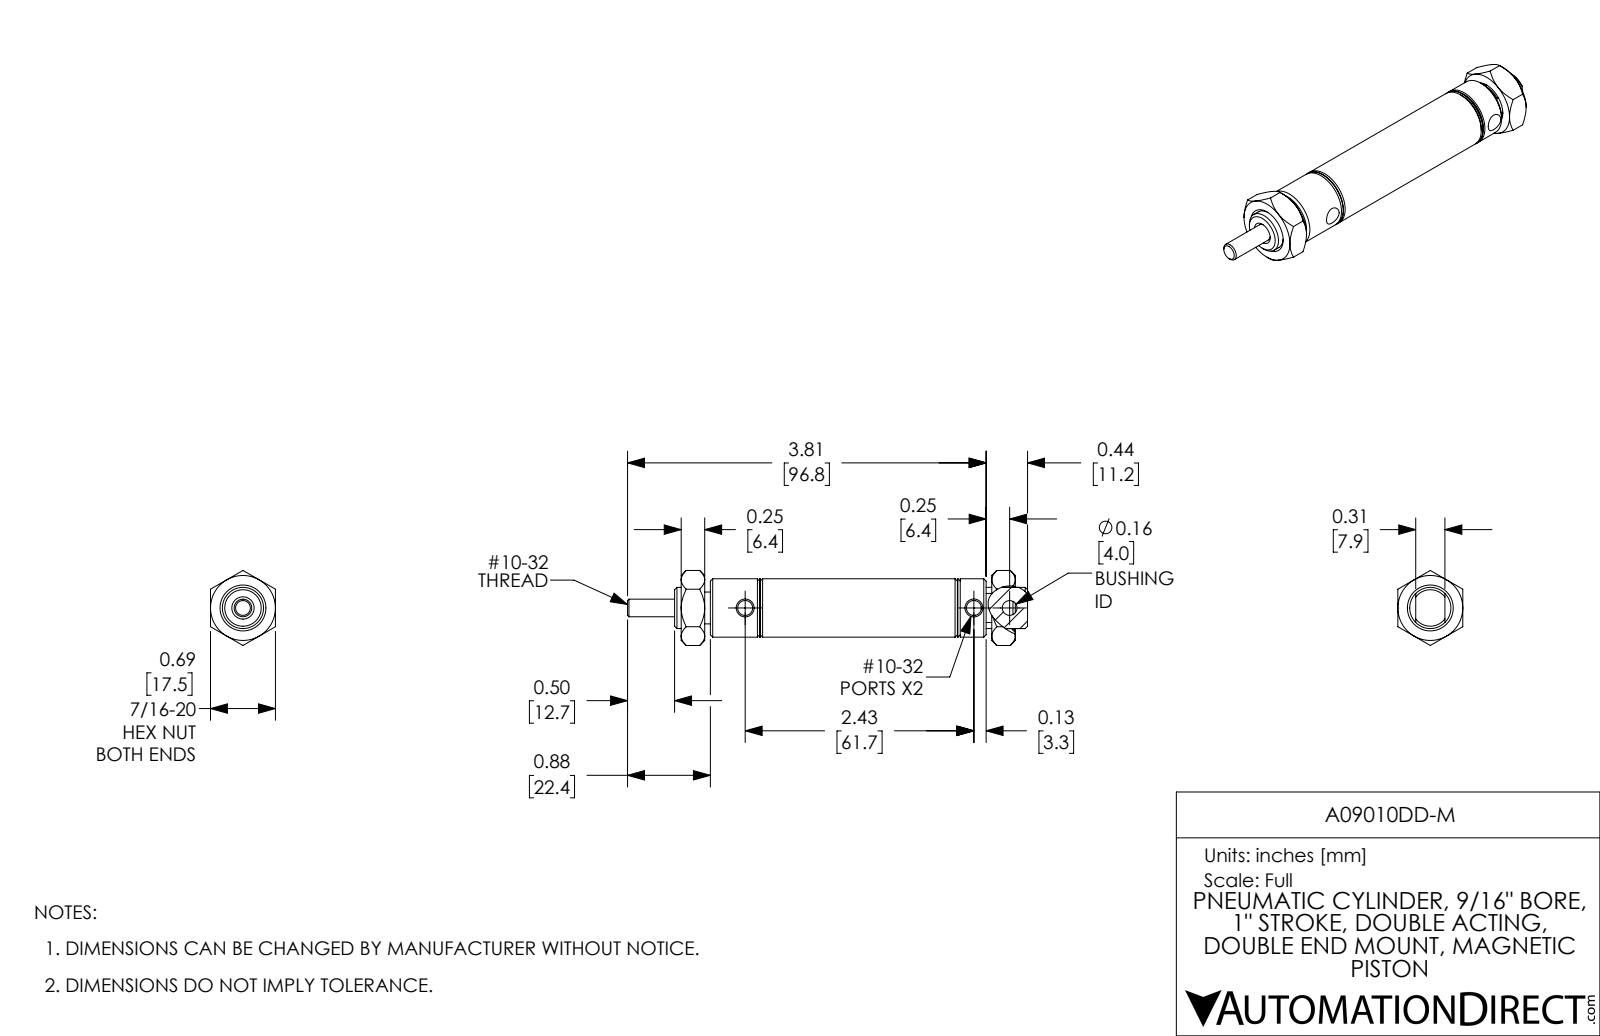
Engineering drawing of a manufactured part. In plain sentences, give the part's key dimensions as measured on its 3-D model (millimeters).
The part is named "A09010DD-M; A09010DD-M_Mounting Nut_D-154; A09010DD-M-Rod; A09010DD-M-MainBody". Its 3-D file was written by "SolidWorks 2017 (AUTOMOTIVE_DESIGN)". It is 4 solids with 151 faces: 36 planar, 46 cylindrical and 69 other. Overall it measures 108 by 20.2 by 17.5 millimeters. Its volume is 14 400 cubic millimeters and its surface area 11 380 square millimeters. Round holes: 2 of diameter 4, 2 of diameter 4.8, 1 of diameter 4, 1 of diameter 4, 1 of diameter 4.7, 1 of diameter 14.3. Round bosses or shafts: 1 of diameter 15.7, 1 of diameter 11.1, 1 of diameter 8.6. The main face-to-face distances are 17.5, 12.7, 6.4, 83.8, 18.2, 56.3, 57.8, 7.9, 38.1, 19.7. The hole center spacings are 9.7, 61.7, 71.4.
